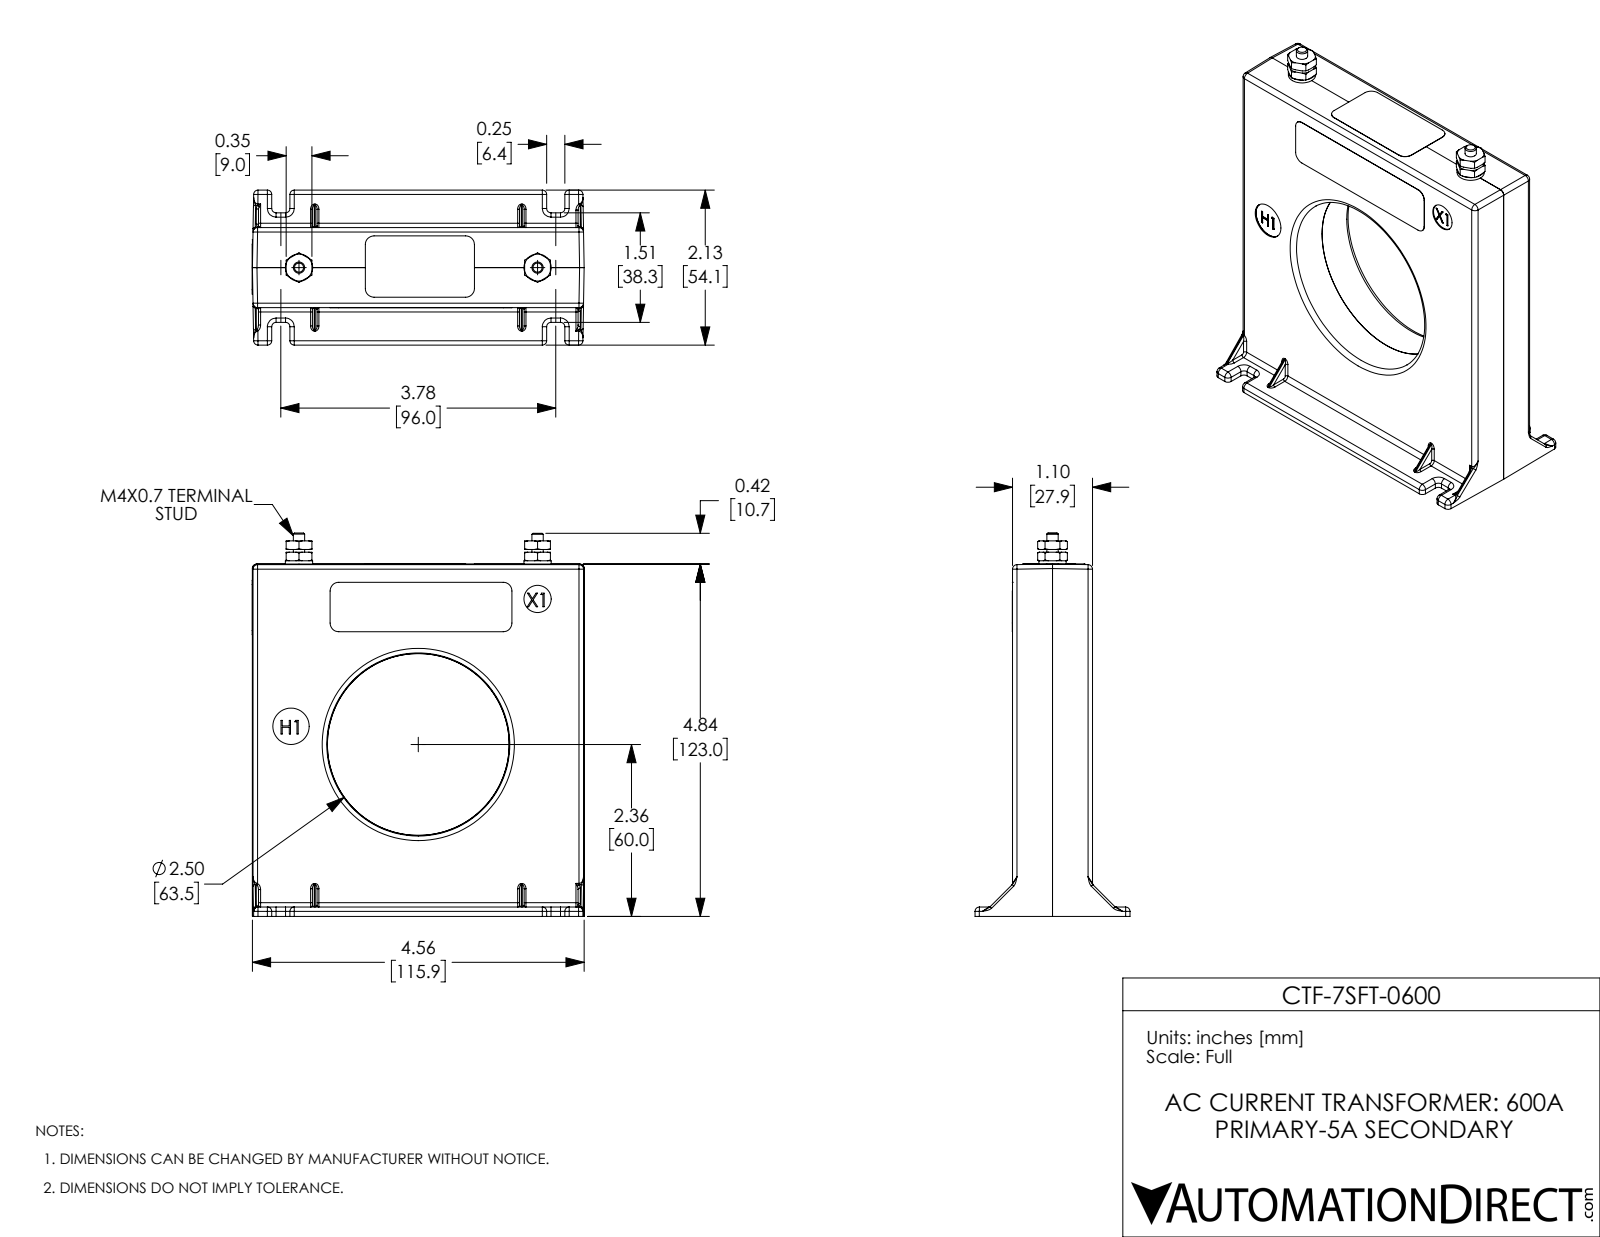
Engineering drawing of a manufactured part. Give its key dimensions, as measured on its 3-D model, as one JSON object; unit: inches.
{"part_name": "CTF-7SFT-0600", "step_written_by": "SolidWorks 2018 (AUTOMOTIVE_DESIGN)", "units": "inches", "bodies": {"solids": 14, "faces": 467, "planar": 172, "cylindrical": 143, "other": 152}, "overall_size": [5.27, 4.605, 2.13], "volume_in3": 19.41, "surface_area_in2": 115.8, "round_holes": [[0.155, 2], [0.165, 2], [0.375, 1], [0.5, 1]], "round_bosses_or_shafts": [[0.375, 2]], "partial_cylinders_radius": [[0.06, 37], [0.025, 25], [0.03, 18], [0.062, 5], [0.063, 5], [0.12, 5]], "face_to_face_distances": [0.55, 1.1, 4.561, 0.13, 0.552, 1.102, 4.843, 4.713, 4.845, 4.715], "hole_center_spacings": [3.28, 3.815]}
